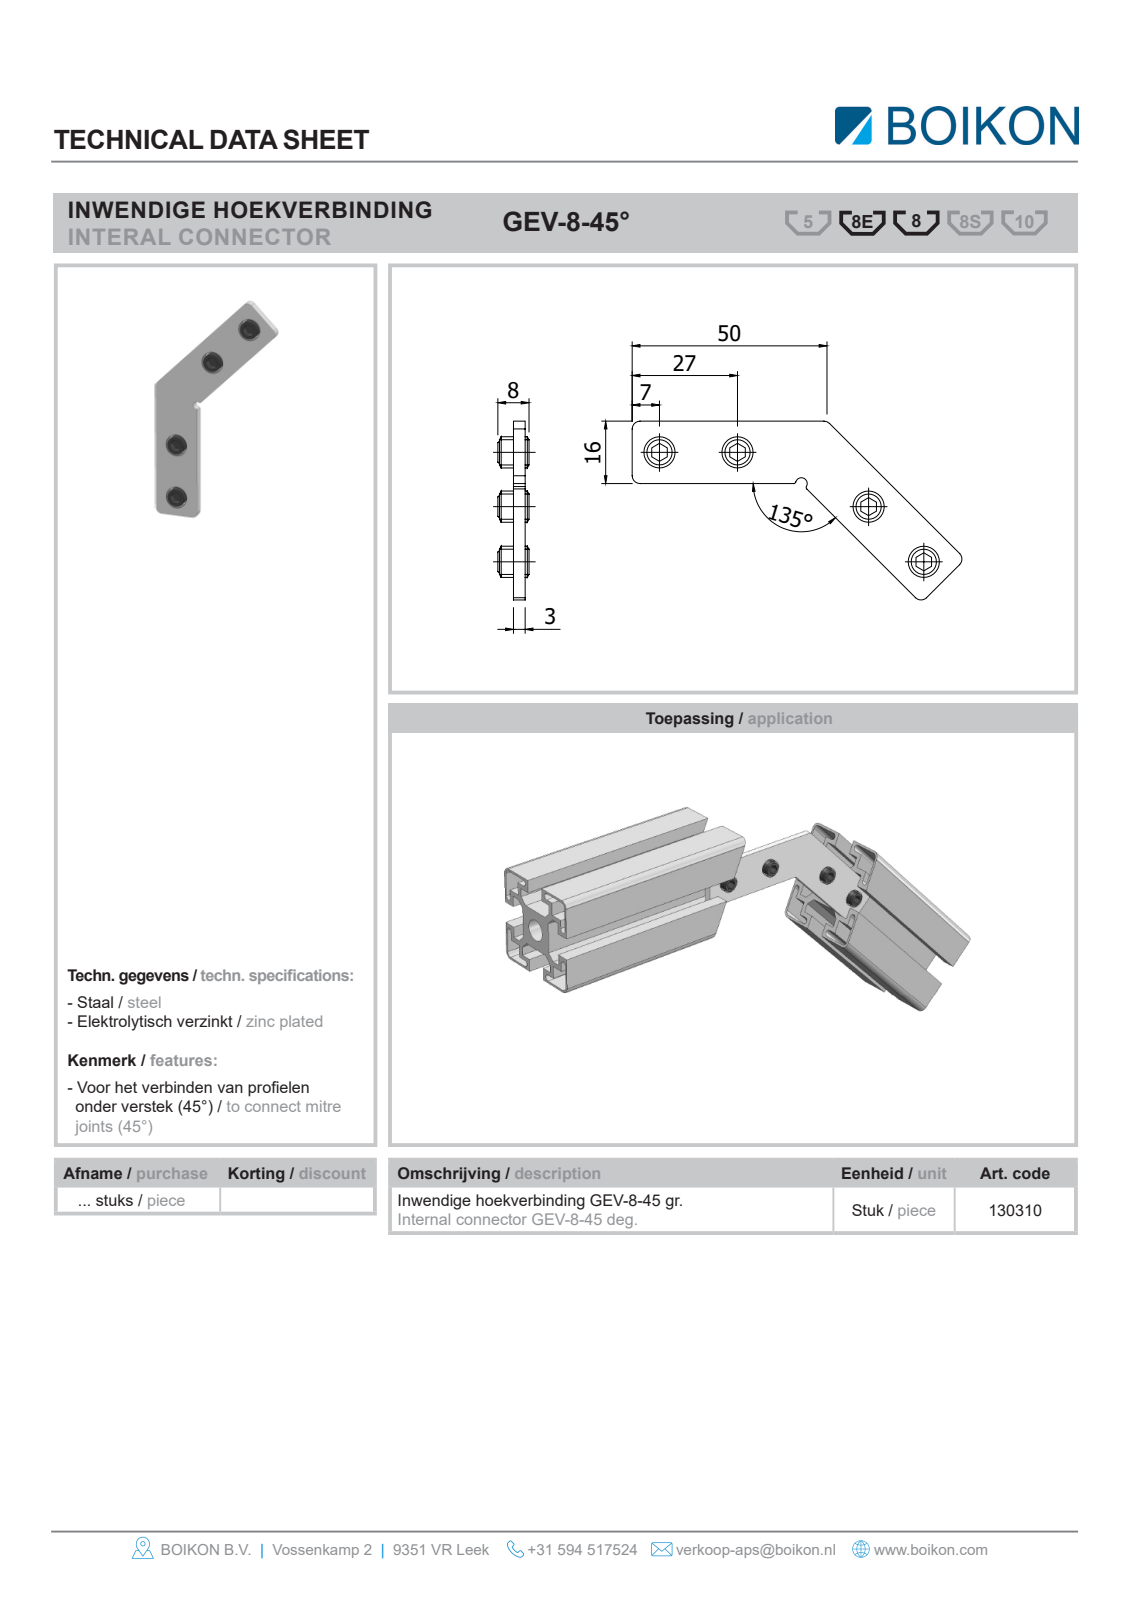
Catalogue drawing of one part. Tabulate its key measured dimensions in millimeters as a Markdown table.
| quantity | value |
| --- | --- |
| part name | Root; 130310Inwendige hoekverbinding GEV-8 45gr.BOIKON; DIN EN ISO 4029-M8x8-45HSet screws0 |
| STEP written by | HiCAD 2013 1802.4 Build 509 (AUTOMOTIVE_DESIGN) |
| units | millimeters |
| bodies | 5 solids, 60 faces (44 planar, 8 cylindrical, 8 other) |
| overall size | 85.36 × 46.67 × 16.3 |
| volume | 4 709 mm³ |
| surface area | 4 612 mm² |
| round holes (diameter × count) | 8 × 4 |
| round bosses / shafts (diameter × count) | 6.47 × 4 |
| main face-to-face distances | 3, 4, 16, 1, 15.99, 2, 10, 7.58, 6.58, 4.58 |
| hole center spacings | 20, 36.38, 55.38, 55.39, 73.33 |
